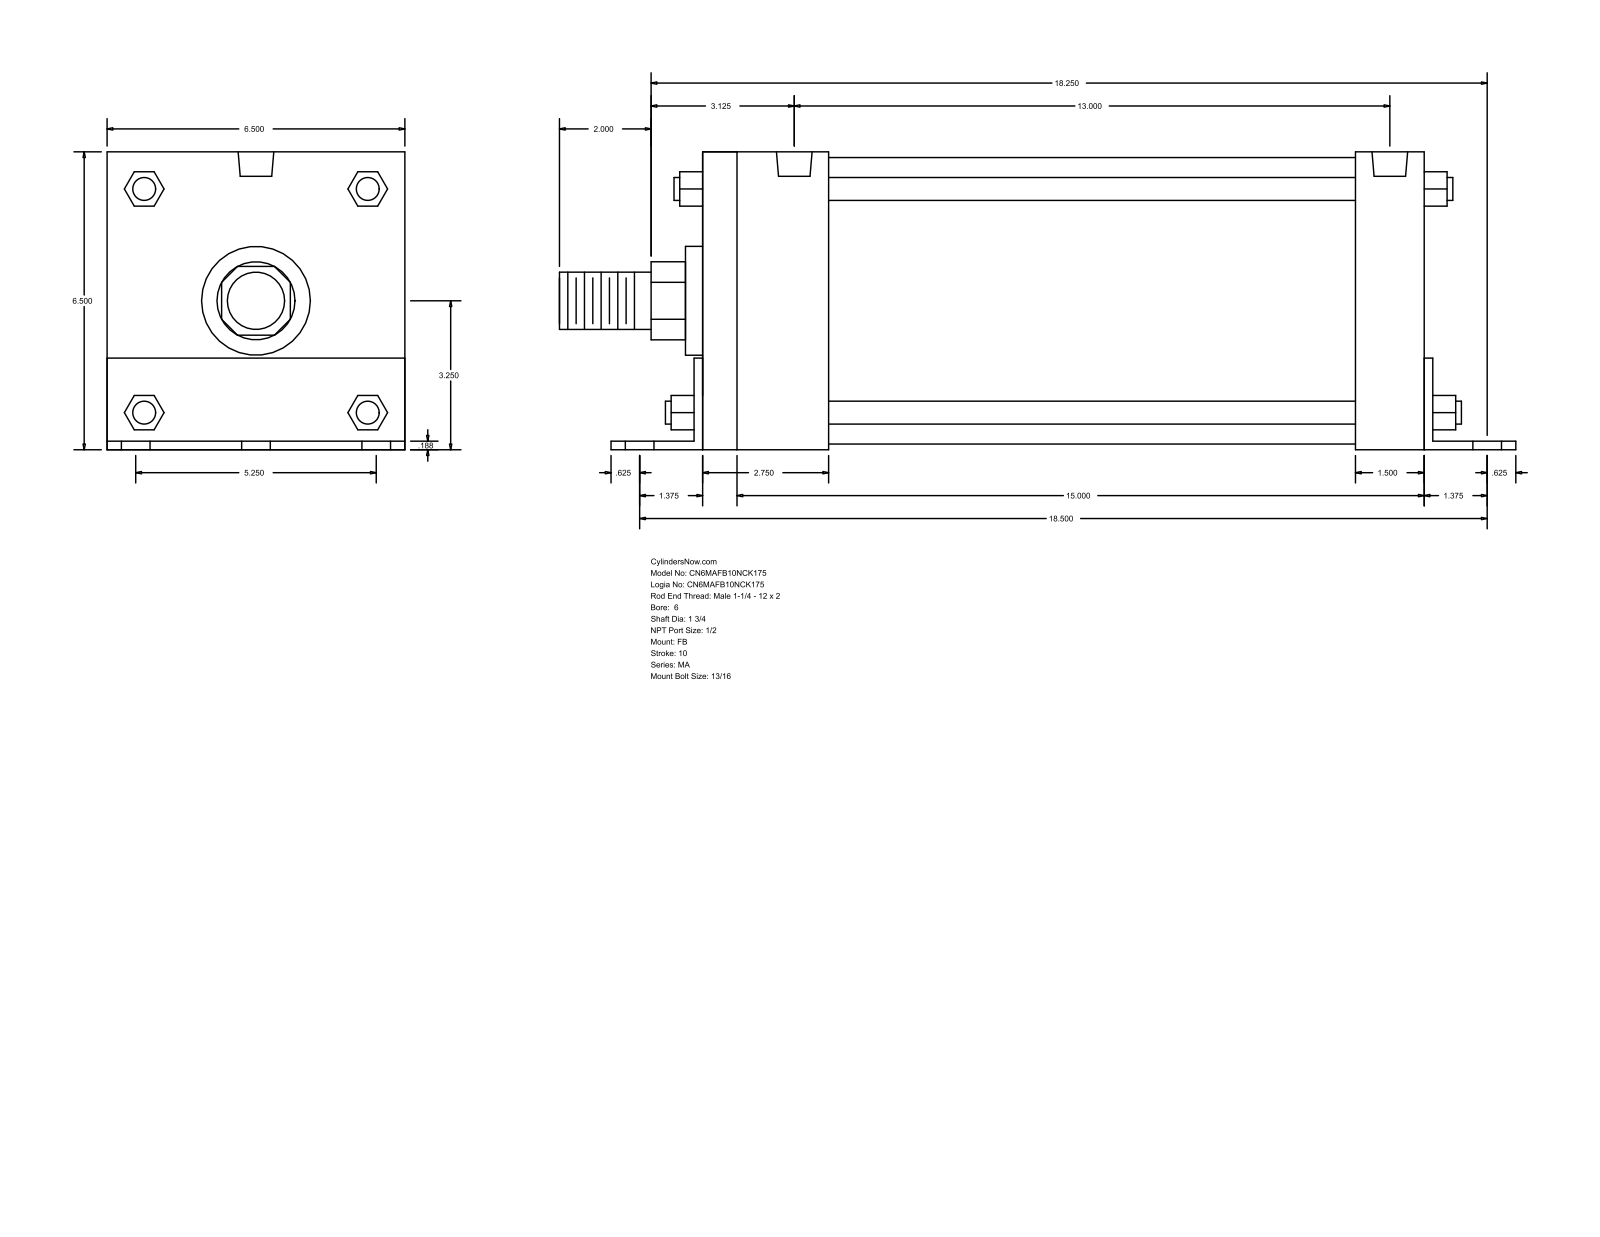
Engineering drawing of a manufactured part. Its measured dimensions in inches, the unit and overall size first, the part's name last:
Units: inches
Overall size (bounding box): 20.875 × 6.502 × 6.5
Round holes (diameter × count): ⌀0.813 ×6, ⌀0.687 ×4, ⌀0.778 ×2
Round bosses / shafts (diameter × count): ⌀0.5 ×4, ⌀6.25 ×1, ⌀2.375 ×1, ⌀1.75 ×1, ⌀1.25 ×1
Partial cylindrical surfaces — rounded edges, fillets, slot ends (radius × count): R0.852 ×1, R1.262 ×1
Main face-to-face distances: 6.5, 0.187, 15.75, 6.502, 0.185, 6.315, 2.75, 2.937, 0.188, 1.5
Hole centre spacings: 2.625, 18.685, 18.5, 3.377, 4.276, 5.25, 13, 15.351
Bodies: 0 solids, 140 faces (105 planar, 35 cylindrical, 0 other)
Part name (STEP PRODUCT): MA_FB__0600_1.75
STEP written by: GSSL Pune (CONFIG_CONTROL_DESIGN)
